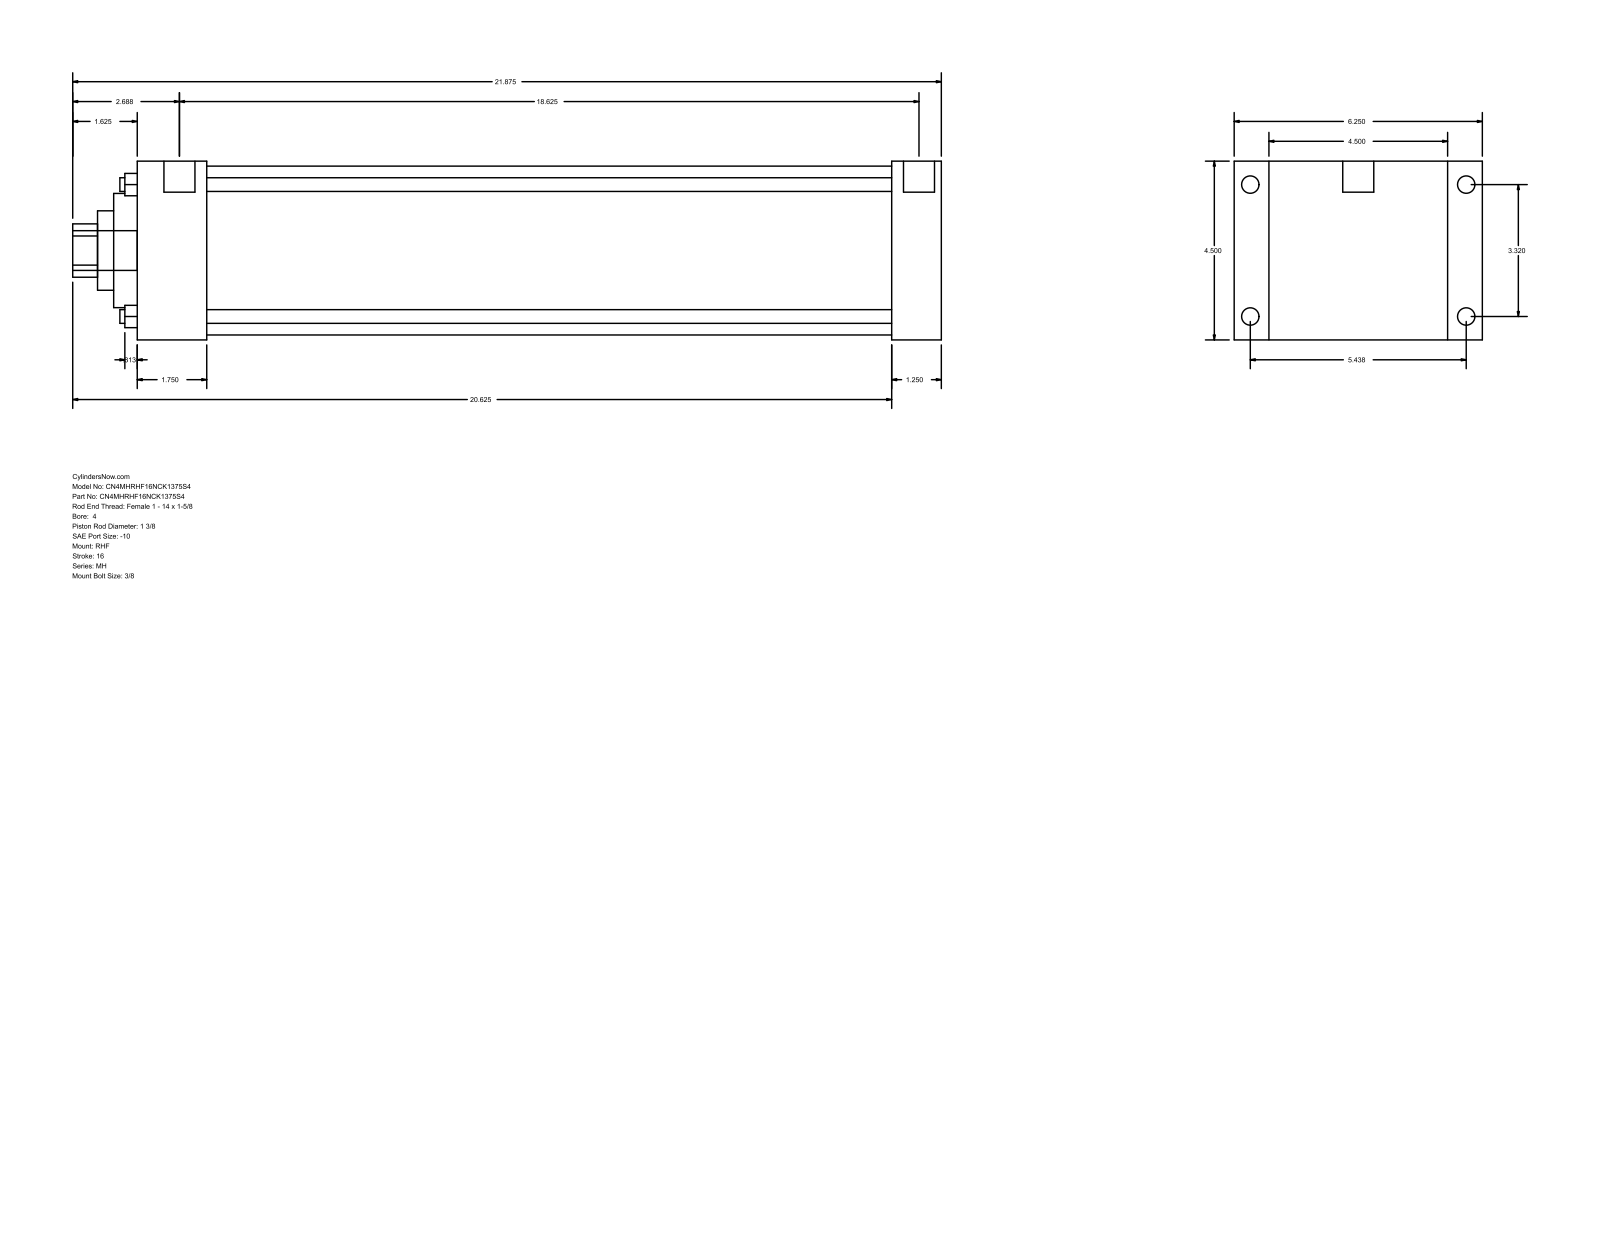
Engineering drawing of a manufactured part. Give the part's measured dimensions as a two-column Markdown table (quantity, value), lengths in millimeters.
| quantity | value |
| --- | --- |
| part name | MH_RHF__0400_1.375 |
| STEP written by | GSSL Pune (CONFIG_CONTROL_DESIGN) |
| units | millimeters |
| bodies | 0 solids, 90 faces (61 planar, 29 cylindrical, 0 other) |
| overall size | 555.62 × 158.75 × 114.3 |
| round holes (diameter × count) | 8.76 × 4, 34.92 × 1, 50.8 × 1, 73.03 × 1, 107.95 × 1 |
| round bosses / shafts (diameter × count) | 11.13 × 4, 8.73 × 4, 19.84 × 2, 25.4 × 1 |
| partial cylindrical surfaces (radius × count) | 17.06 × 1 |
| main face-to-face distances | 114.3, 514.35, 482.61, 31.74, 22.23, 136.53, 44.45, 438.16, 469.9, 158.76 |
| hole center spacings | 59.62, 84.32, 119.25 |
